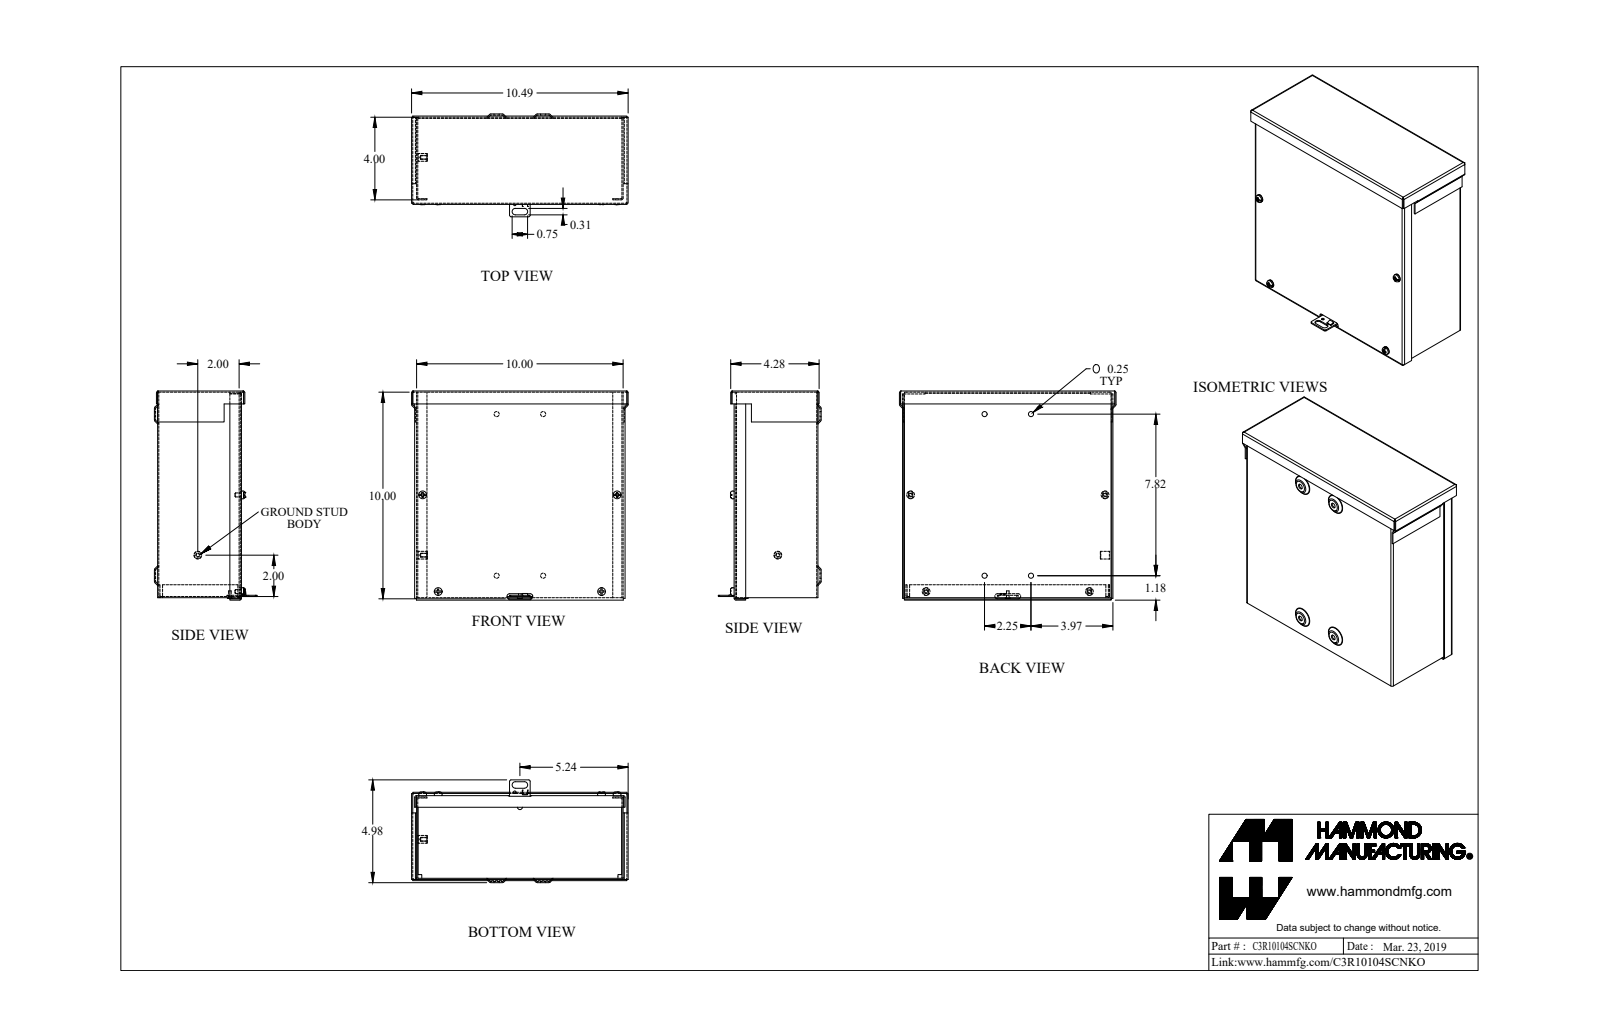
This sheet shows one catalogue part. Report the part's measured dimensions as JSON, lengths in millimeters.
{"part_name": "C3R10104SCNKO_Default", "step_written_by": "SolidWorks 2019 (CONFIG_CONTROL_DESIGN)", "units": "millimeters", "bodies": {"solids": 11, "faces": 404, "planar": 211, "cylindrical": 107, "other": 86}, "overall_size": [266.4, 257, 126.4], "volume_mm3": 399000, "surface_area_mm2": 557600, "round_holes": [[4.3, 4], [6.4, 4], [3.2, 1], [3.5, 1], [4, 1]], "round_bosses_or_shafts": [[9.5, 4], [4.8, 4], [9.5, 1], [3.2, 1]], "partial_cylinders_radius": [[0.7, 21], [2.2, 21], [2.8, 8], [3.2, 8], [4, 2]], "face_to_face_distances": [1.4, 101.6, 100.2, 252.6, 103, 254, 1.4, 251.1, 251.1, 252.6], "hole_center_spacings": [134.7, 178.3, 57.2, 74.4, 120.4, 130.5, 198.6, 206.6]}
